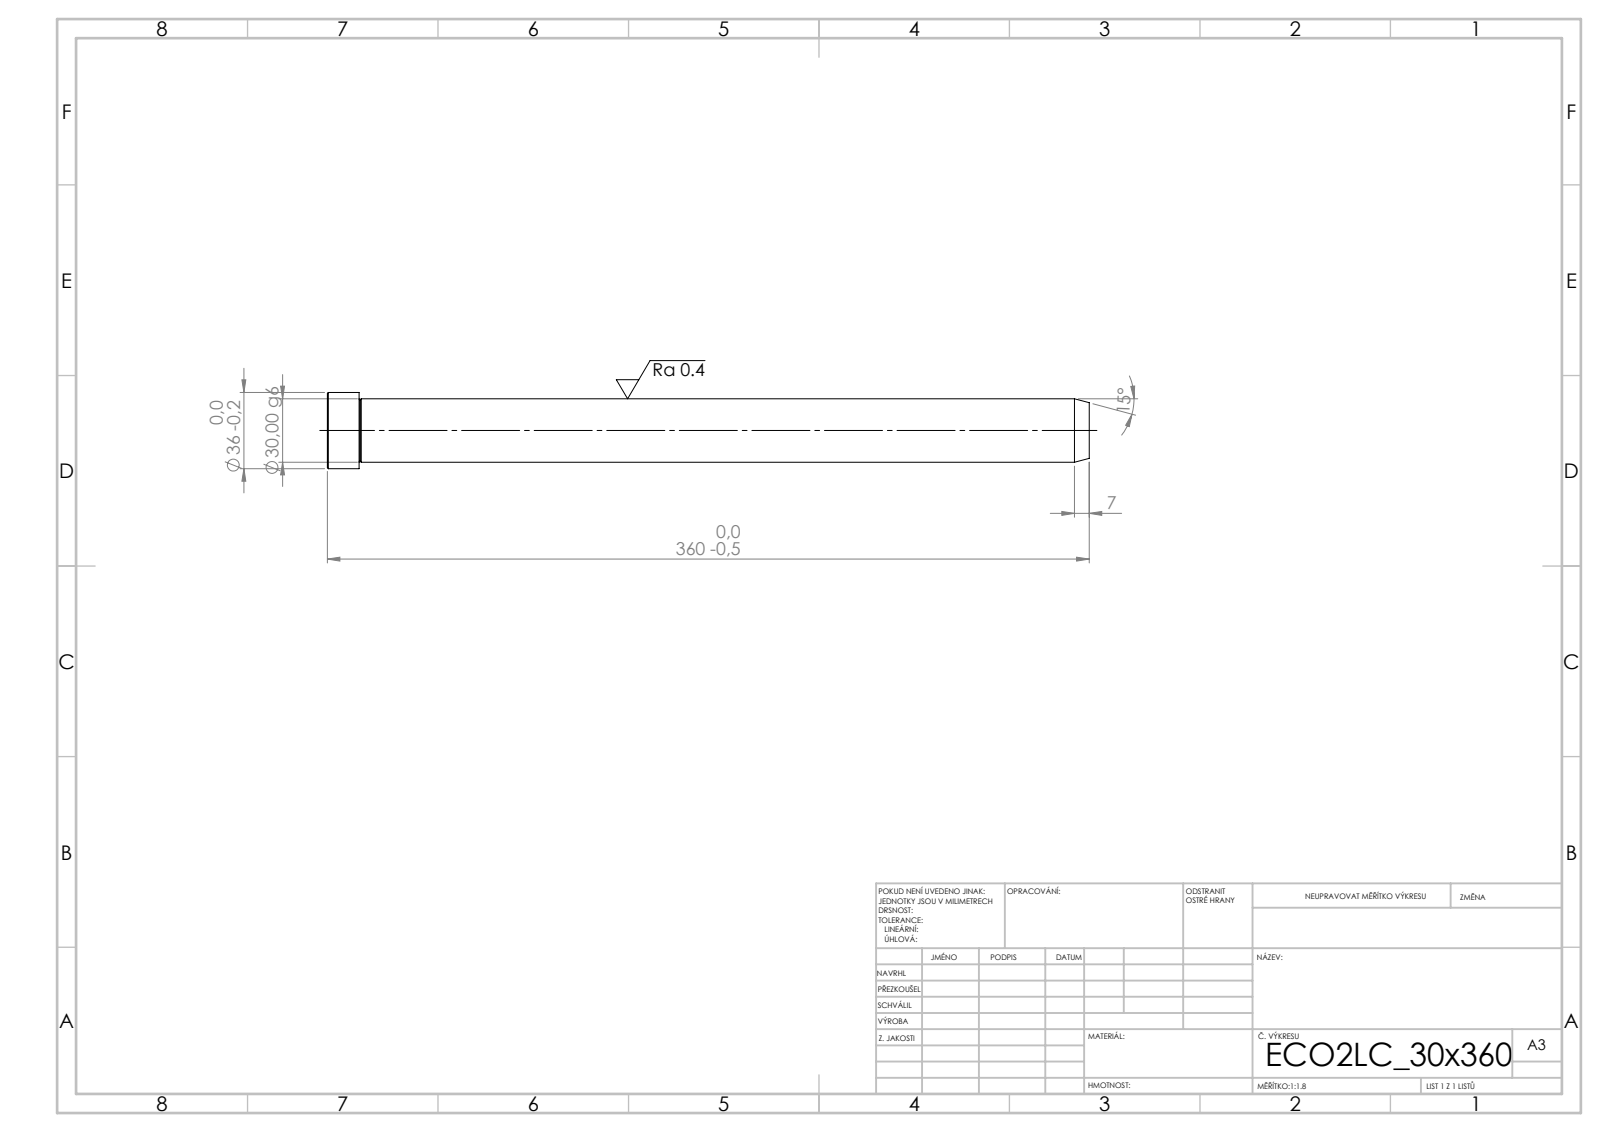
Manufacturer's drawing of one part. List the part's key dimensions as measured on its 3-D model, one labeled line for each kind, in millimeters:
STEP written by: SolidWorks 2019 (CONFIG_CONTROL_DESIGN)
Units: millimetres
Bodies: 1 solid, 15 faces (3 planar, 4 cylindrical, 8 other)
Overall size (bounding box): 360 × 36 × 36
Volume: 258 491 mm³ · Surface area: 36 080 mm²
Round bosses / shafts (diameter × count): ⌀36 ×1, ⌀30 ×1
Main face-to-face distances: 360, 345, 15
